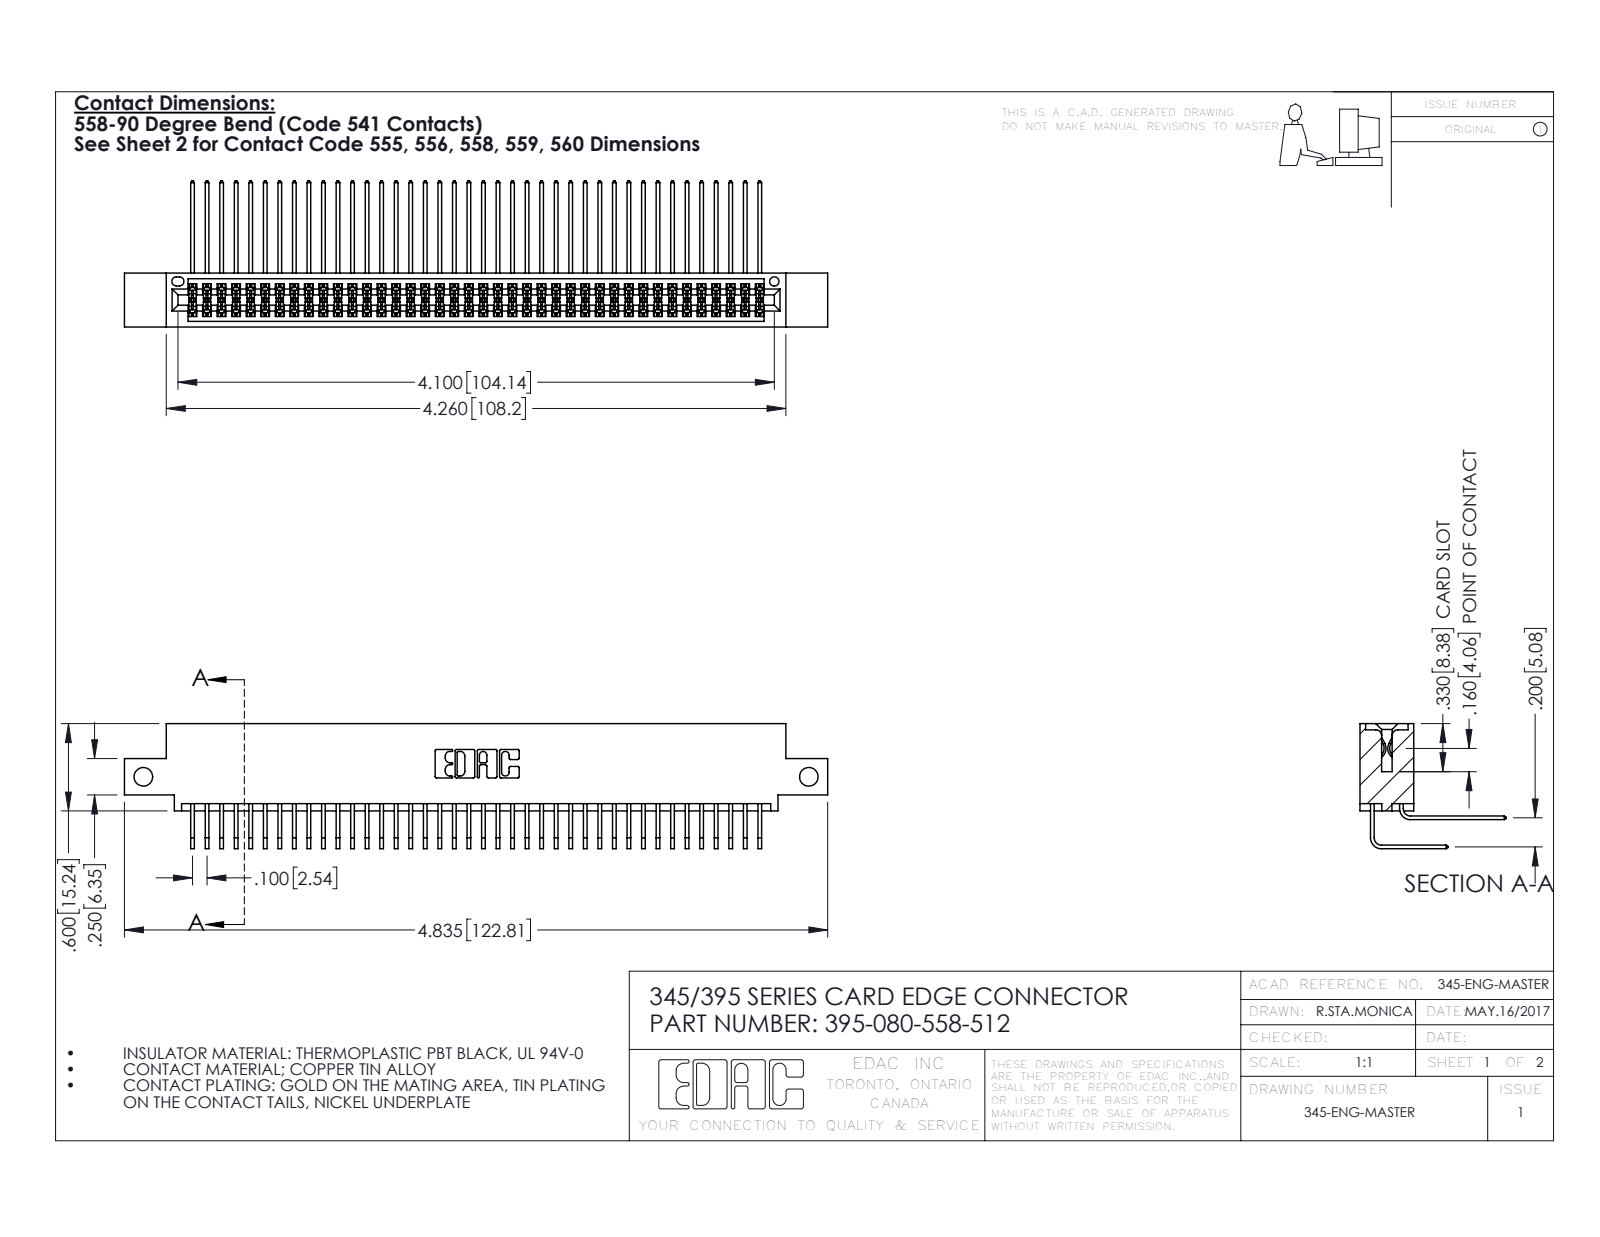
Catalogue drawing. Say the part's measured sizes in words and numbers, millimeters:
The part is named "345 Part_0.110 Offset - Side Mount; 345-292-001_558 559 Tail - 1; 395-080-558-512; 345-292-001_558 Tail - 2". Its 3-D file was written by "SolidWorks 2016 (CONFIG_CONTROL_DESIGN)". It is 81 solids with 4290 faces: 2884 planar, 1406 cylindrical and 0 other. Overall it measures 122.8 by 25.5 by 21.8 millimeters. Its volume is 12 200 cubic millimeters and its surface area 20 140 square millimeters. Round holes: 2 of diameter 3.3, 1 of diameter 1.6. Partial cylindrical surfaces (rounded edges, fillets, slot ends): 121 of radius 0.2, 22 of radius 0.3, 6 of radius 0.2, 6 of radius 0.8, 3 of radius 0.7, 2 of radius 0.4, 2 of radius 0.5, 2 of radius 0.6. The main face-to-face distances are 1.8, 7.6, 5.1, 9.4, 2.5, 6.9, 0.6, 5.7, 0.6, 4.4. The hole center spacings are 116.2.
